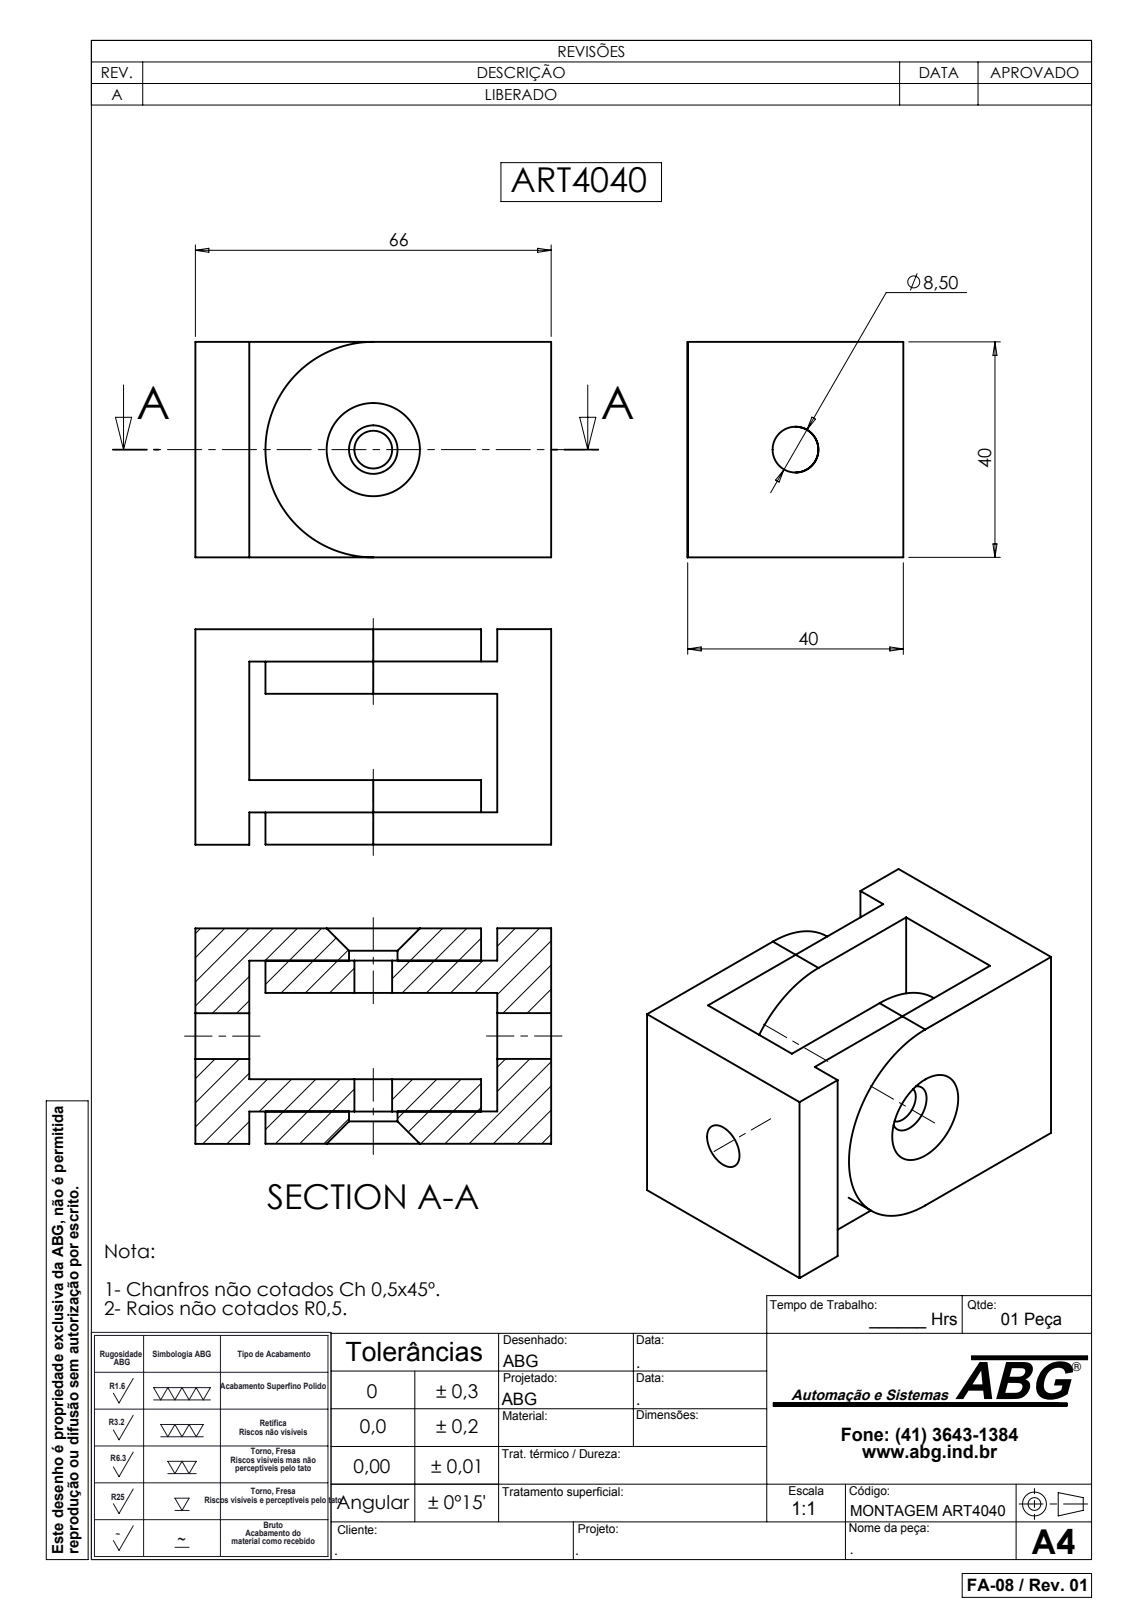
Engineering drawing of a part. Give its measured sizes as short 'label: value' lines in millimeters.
name: ART4040
written by: SolidWorks 2007 (CONFIG_CONTROL_DESIGN)
unit: mm
bodies: 1 solid, 20 faces (10 planar, 8 cylindrical, 2 other)
size: 53 × 40 × 40
volume: 33 081 mm³; area: 12 024 mm²
holes: 1× ⌀7, 1× ⌀8.5, 1× ⌀9
rounds: 1× R20
face distances: 6, 28, 34, 22, 40, 10, 12
